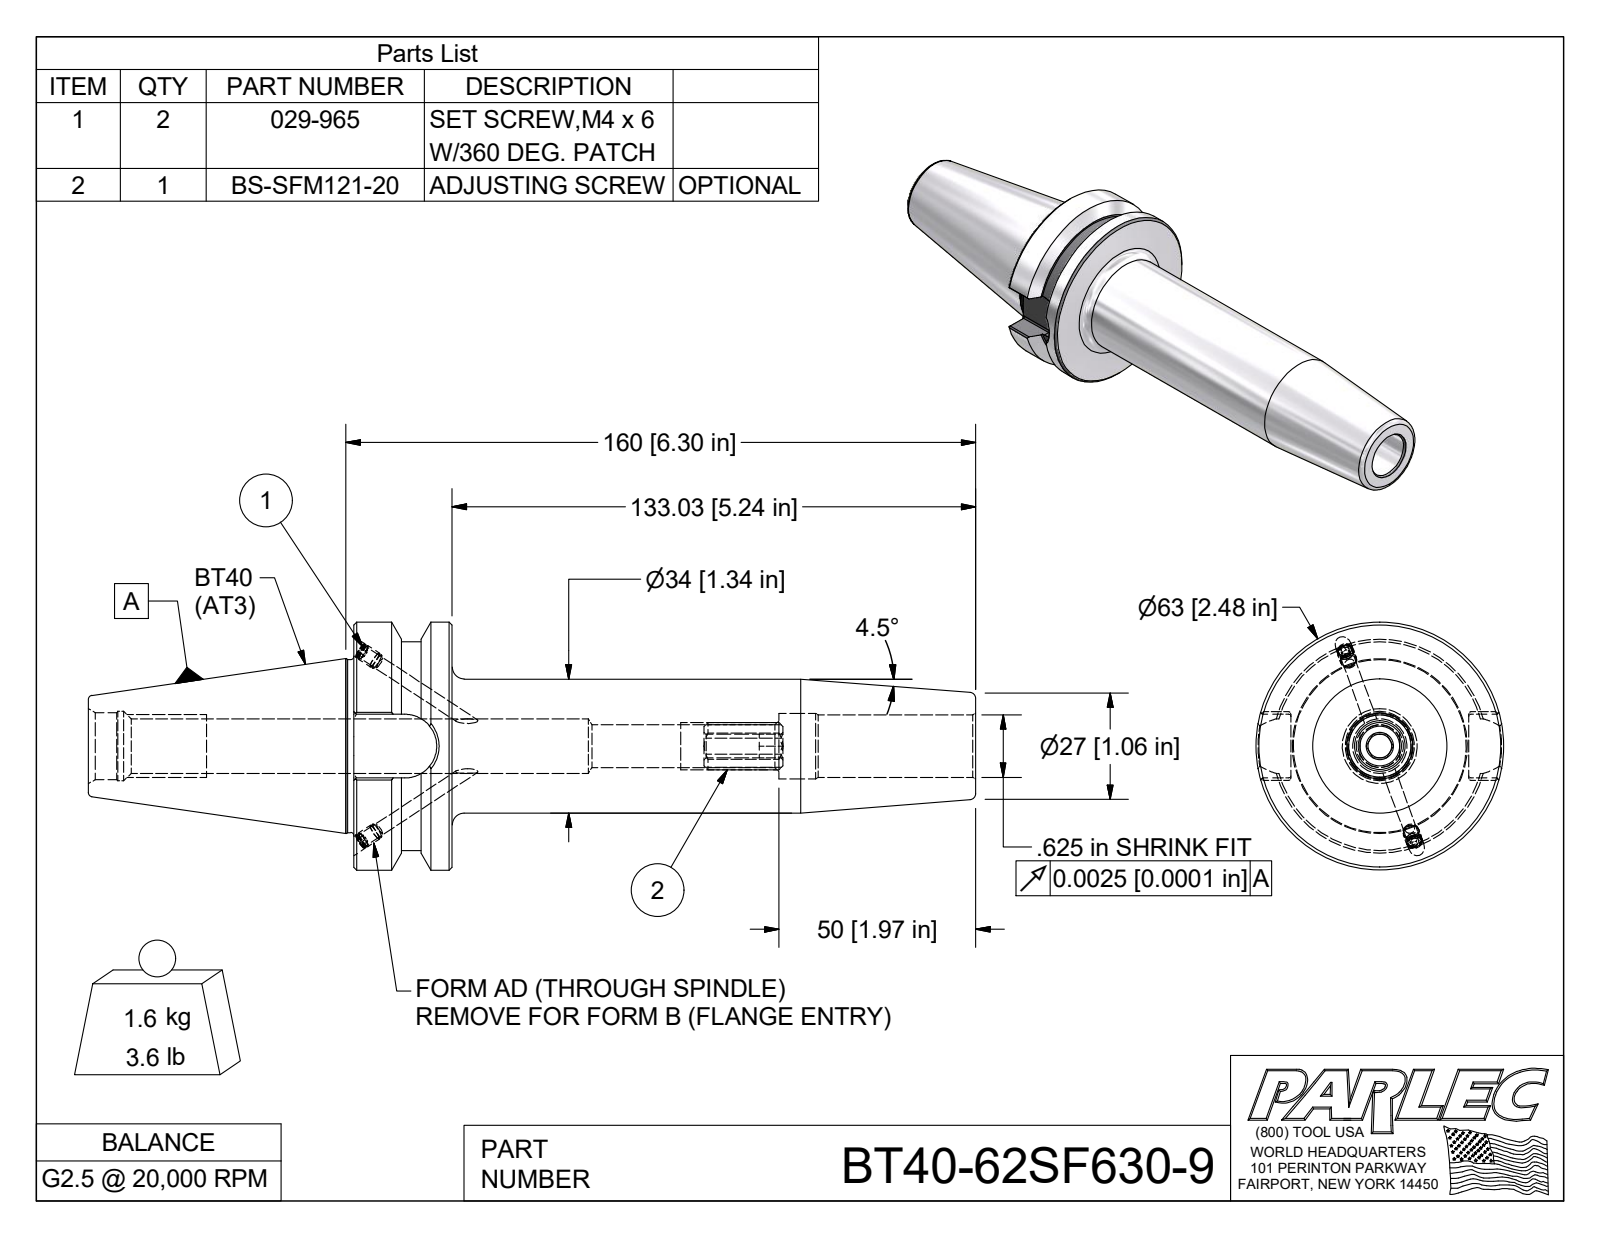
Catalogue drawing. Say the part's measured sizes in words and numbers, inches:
The part is named "BT40-62SF630-9; BT40BC-62SF630-9-1; 029-965; BS-SFM121-20". Its 3-D file was written by "Autodesk Inventor 2009 (AUTOMOTIVE_DESIGN)". It is 4 solids with 131 faces: 57 planar, 33 cylindrical and 41 other. Overall it measures 8.874 by 2.48 by 2.48 inches. Its volume is 13.04 cubic inches and its surface area 67.27 square inches. Round holes: 2 of diameter 0.13, 2 of diameter 0.161, 1 of diameter 0.624, 1 of diameter 0.654, 1 of diameter 0.694. Round bosses or shafts: 2 of diameter 0.165, 2 of diameter 0.157, 1 of diameter 2.48, 1 of diameter 2.087, 1 of diameter 1.75, 1 of diameter 1.73, 1 of diameter 1.339. Partial cylindrical surfaces (rounded edges, fillets, slot ends): 8 of radius 0.02, 1 of radius 0.236, 1 of radius 0.319. The main face-to-face distances are 0.984, 1.78, 0.693, 1.087, 6.221, 5.237, 2.653, 3.637, 8.874, 0.637.
